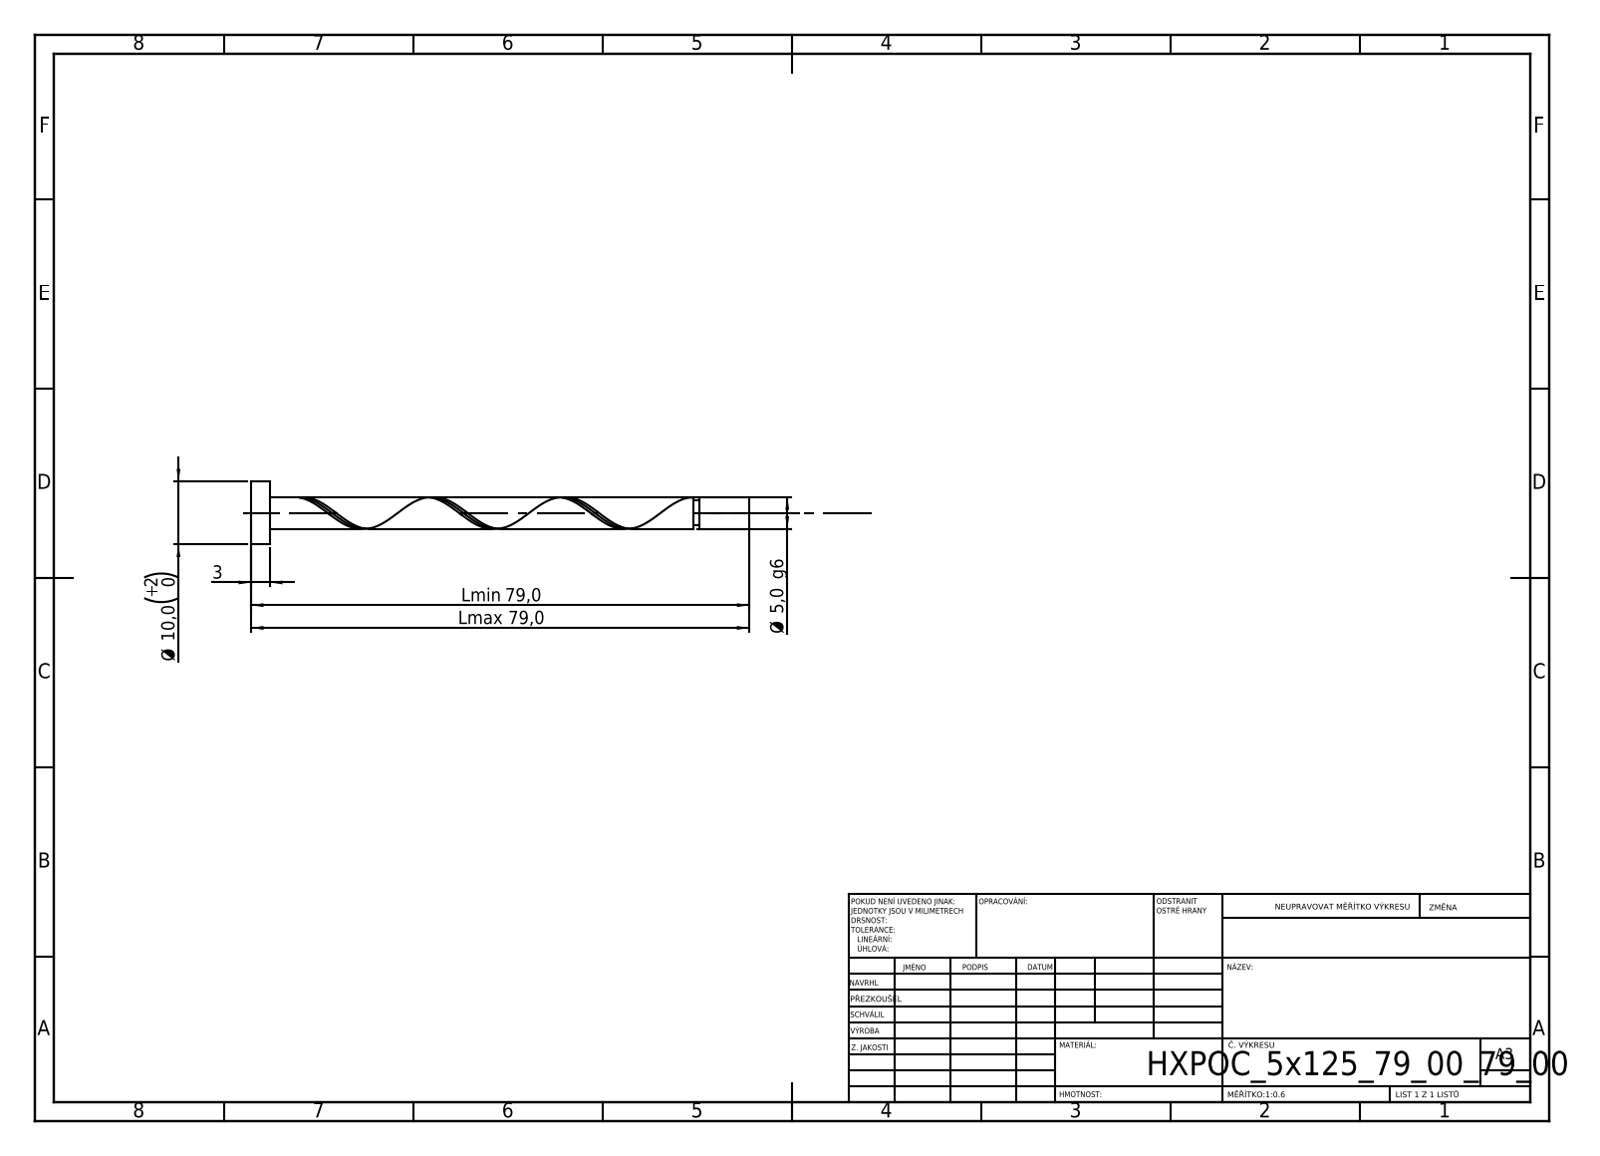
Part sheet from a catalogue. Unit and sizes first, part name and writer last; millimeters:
Units: millimetres
Overall size (bounding box): 79 × 10 × 10
Round bosses / shafts (diameter × count): ⌀10 ×1, ⌀5 ×1, ⌀4 ×1
Main face-to-face distances: 3, 79, 76, 71.11, 68.11, 7.89, 70.11, 67.11, 1, 8.89
Volume: 1 697 mm³ · Surface area: 1 497 mm²
Bodies: 1 solid, 21 faces (6 planar, 14 cylindrical, 1 other)
STEP written by: SolidWorks 2019 (CONFIG_CONTROL_DESIGN)
